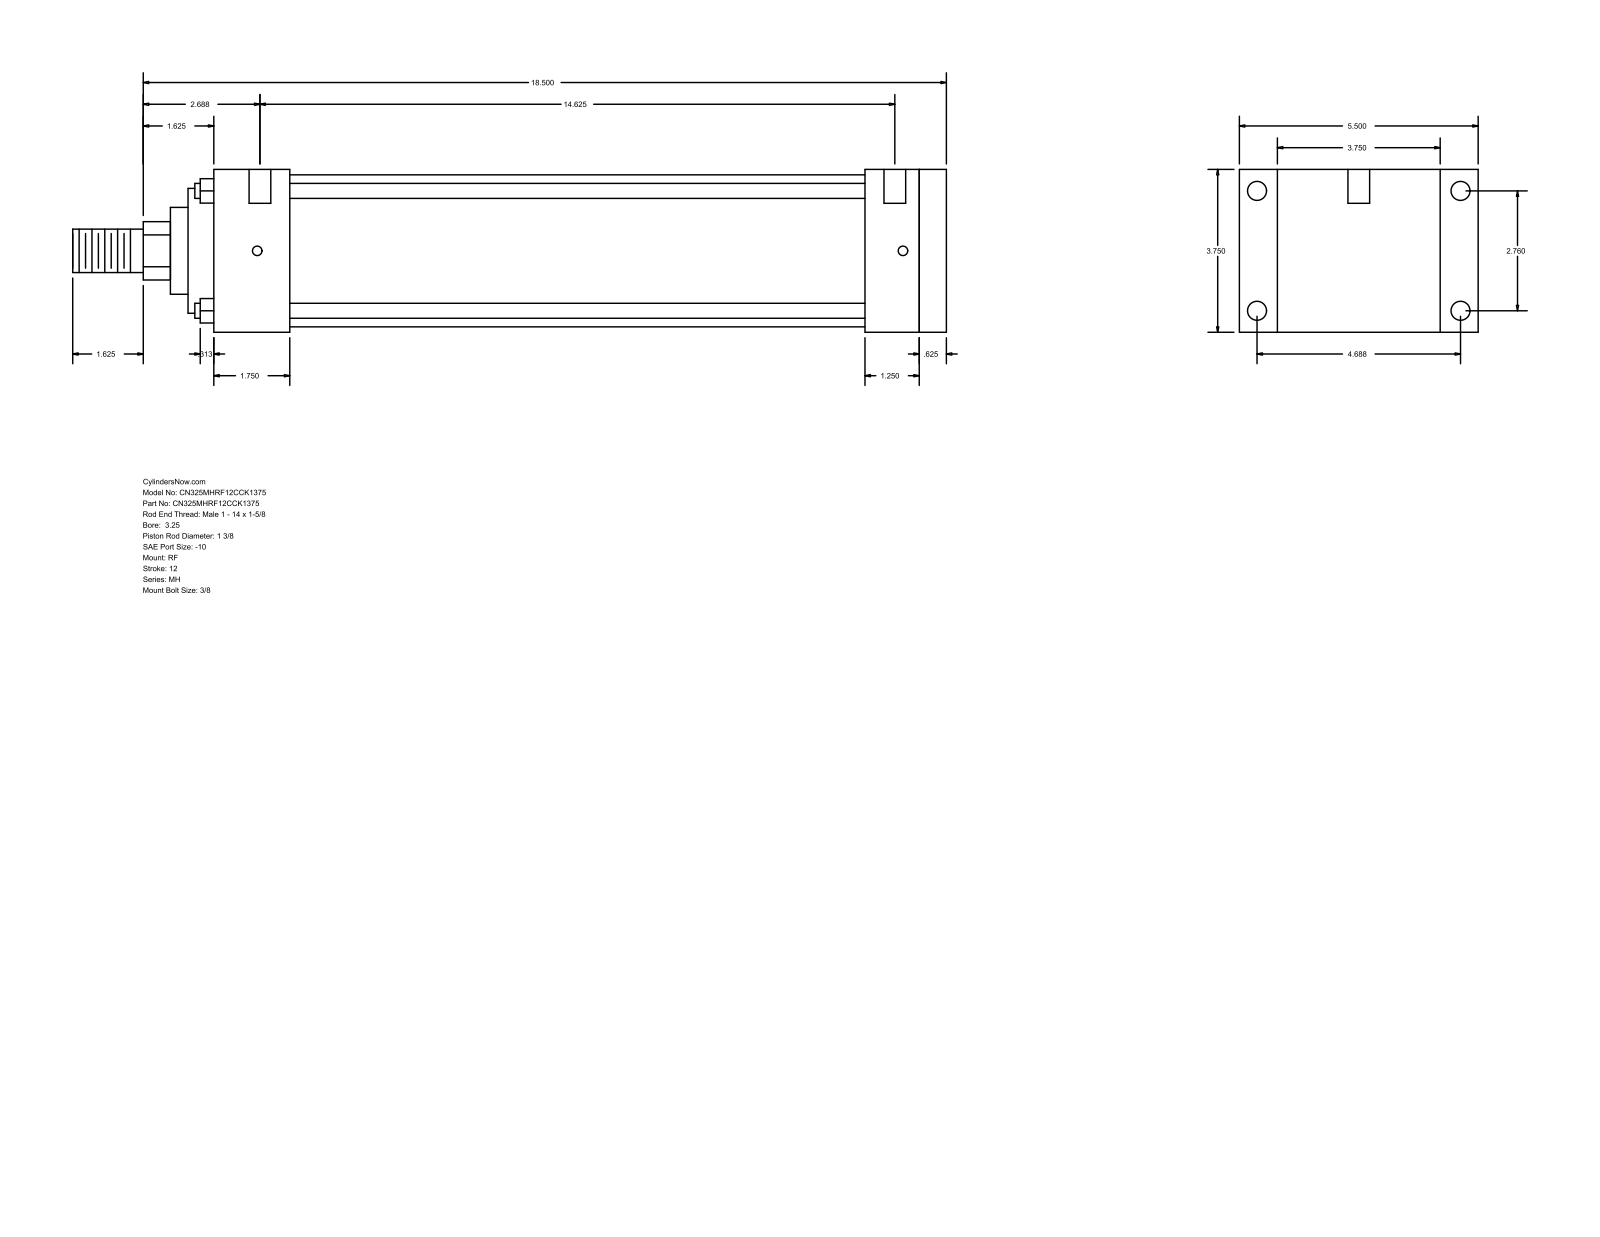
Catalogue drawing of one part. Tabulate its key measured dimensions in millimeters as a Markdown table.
| quantity | value |
| --- | --- |
| part name | MH_RF__0325_1.375 |
| STEP written by | GSSL Pune (CONFIG_CONTROL_DESIGN) |
| units | millimeters |
| bodies | 0 solids, 94 faces (65 planar, 29 cylindrical, 0 other) |
| overall size | 511.18 × 139.7 × 95.25 |
| round holes (diameter × count) | 5.56 × 4, 11.13 × 4, 12.7 × 2 |
| round bosses / shafts (diameter × count) | 8.76 × 4, 88.9 × 1, 73.03 × 1, 50.8 × 1, 34.92 × 1, 25.4 × 1 |
| partial cylindrical surfaces (radius × count) | 17.06 × 1 |
| main face-to-face distances | 95.24, 428.63, 15.88, 412.75, 22.23, 117.47, 44.45, 368.3, 384.18, 381 |
| hole center spacings | 70.1, 119.06, 138.16, 377.83, 1.59, 4.76, 371.48, 373.07 |
